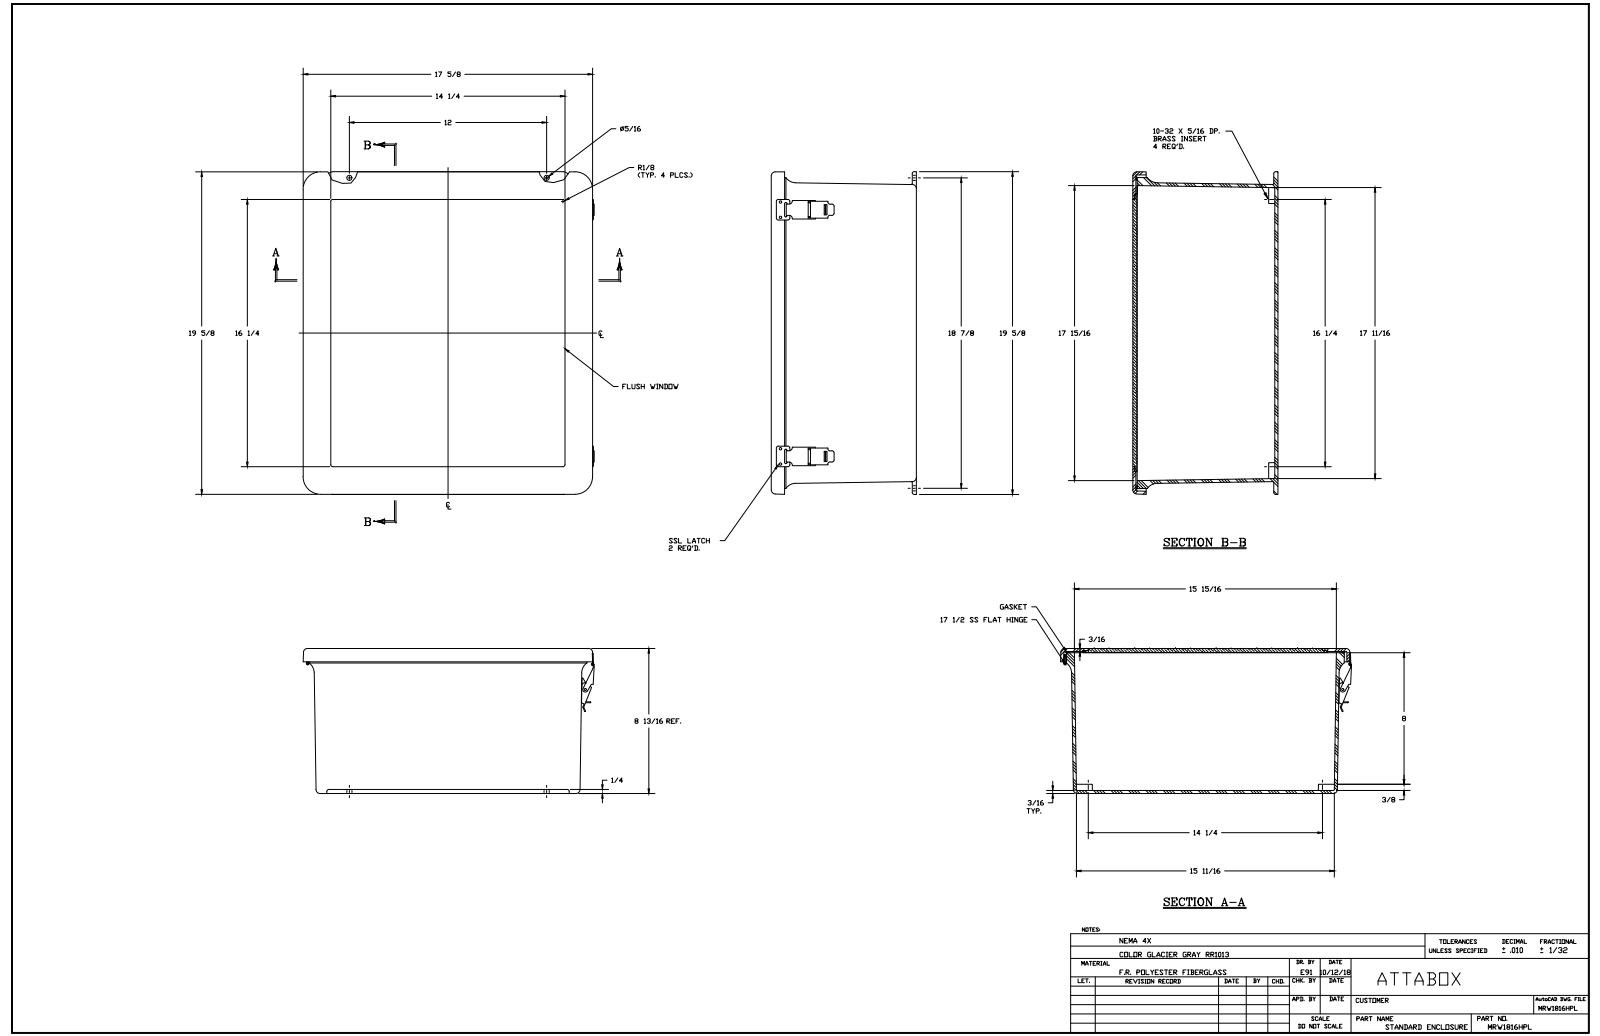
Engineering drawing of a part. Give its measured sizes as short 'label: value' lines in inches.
name: MRW1816HPL
written by: SolidWorks 2018 (AUTOMOTIVE_DESIGN)
unit: in
bodies: 43 solids, 1210 faces (556 planar, 503 cylindrical, 151 other)
size: 19.625 × 17.819 × 8.811
volume: 275.9 in³; area: 2 795 in²
holes: 24× ⌀0.14, 12× ⌀0.131, 5× ⌀0.152, 4× ⌀0.13, 4× ⌀0.156, 4× ⌀0.218, 3× ⌀0.135, 2× ⌀0.375, 1× ⌀0.085
bosses: 20× ⌀0.25, 11× ⌀0.125, 9× ⌀0.125, 4× ⌀0.27, 2× ⌀0.135, 1× ⌀0.155, 1× ⌀0.115, 1× ⌀0.085
rounds: 24× R0.125, 20× R0.015, 20× R0.031, 13× R0.03, 12× R0.25, 10× R0.06, 9× R0.09, 8× R0.005
face distances: 0.188, 0.187, 8.624, 8.811, 0.25, 8.561, 8.374, 0.063, 8.437, 0.302
hole spacings: 3.375, 3.375, 6.75, 10, 9.75, 10.25, 14.984, 0.25
